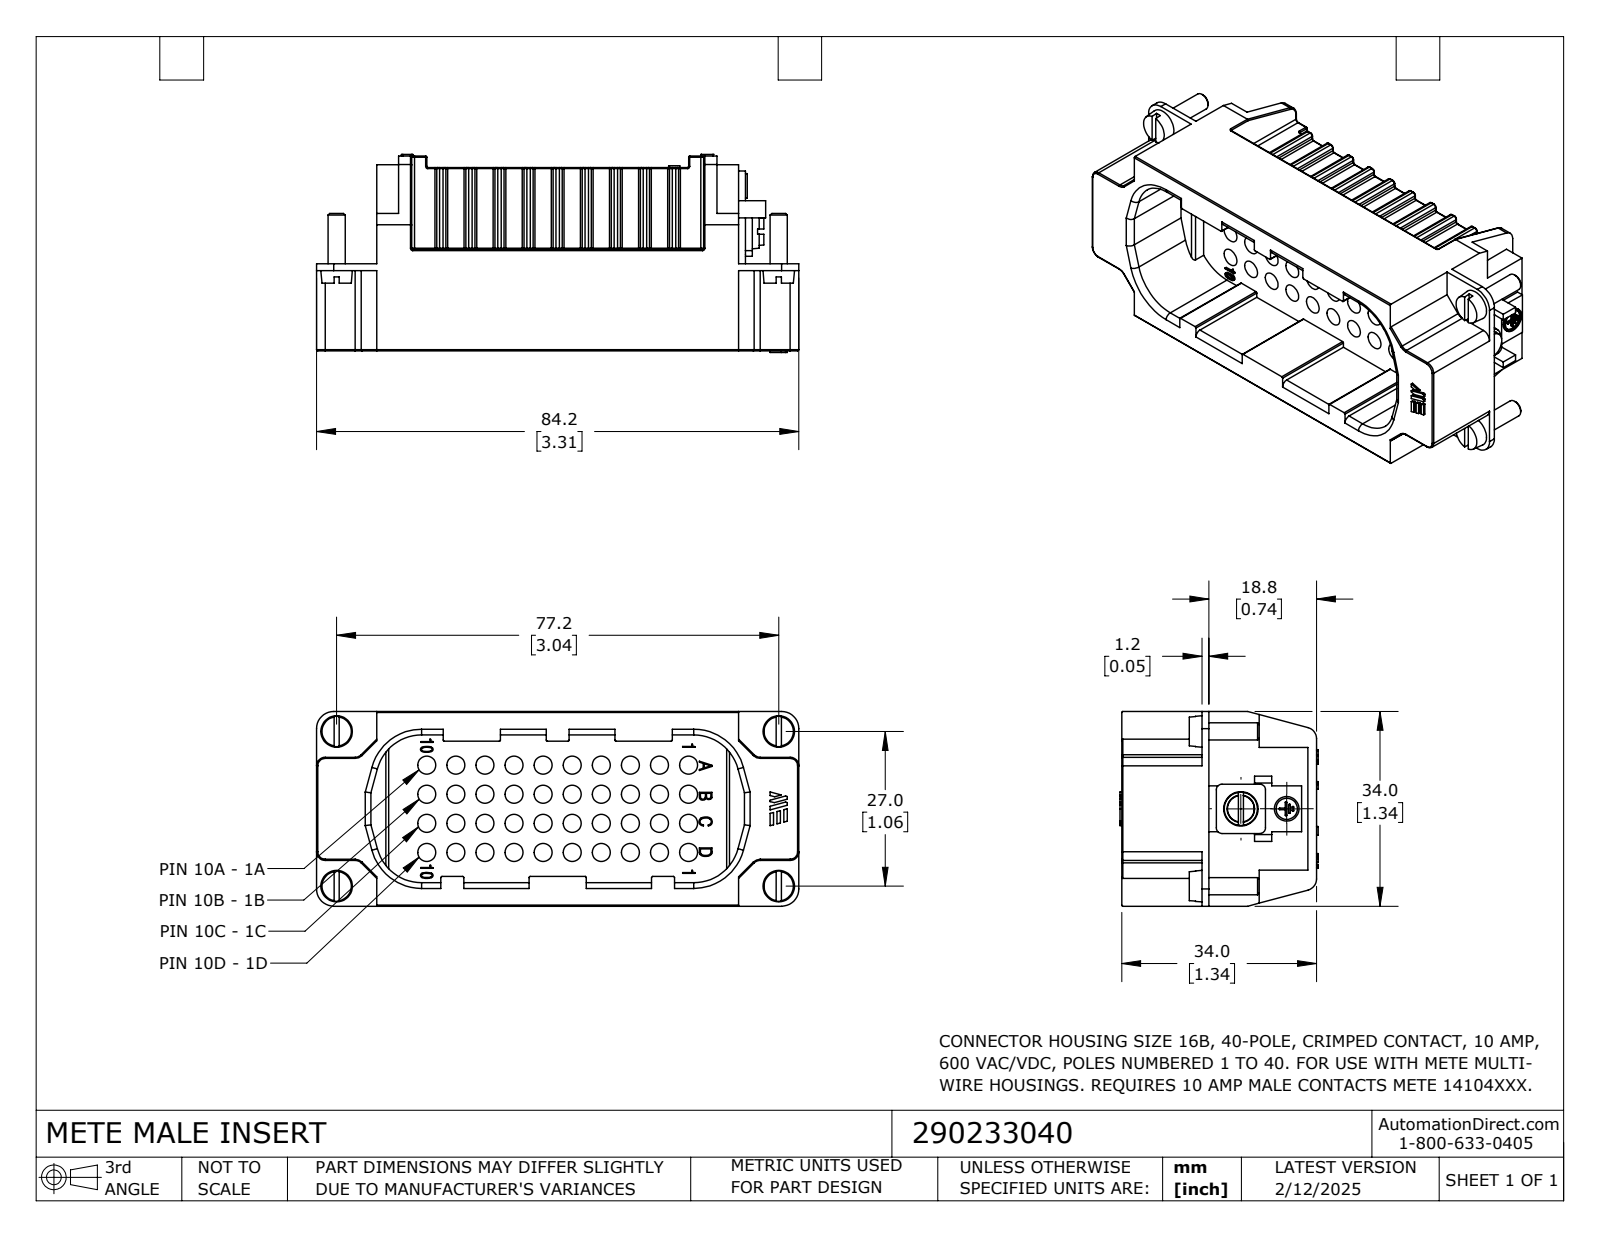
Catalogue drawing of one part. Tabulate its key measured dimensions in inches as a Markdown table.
| quantity | value |
| --- | --- |
| part name | 290233040 |
| STEP written by | SolidWorks 2024 (CONFIG_CONTROL_DESIGN) |
| units | inches |
| bodies | 1 solid, 1139 faces (386 planar, 452 cylindrical, 301 other) |
| overall size | 3.315 × 1.362 × 1.339 |
| volume | 2.343 in³ |
| surface area | 35.38 in² |
| round holes (diameter × count) | 0.124 × 40, 0.146 × 1 |
| round bosses / shafts (diameter × count) | 0.118 × 4, 0.169 × 1 |
| partial cylindrical surfaces (radius × count) | 0.008 × 90, 0.02 × 42, 0.012 × 36, 0.004 × 14, 0.039 × 12, 0.059 × 8, 0.085 × 8, 0.118 × 4 |
| main face-to-face distances | 1.339, 0.043, 0.248, 0.929, 1.091, 0.591, 0.087, 0.563, 0.161, 1.177 |
| hole center spacings | 0.447, 0.632, 0.2, 0.4, 0.721, 0.283, 0.6, 0.825 |
